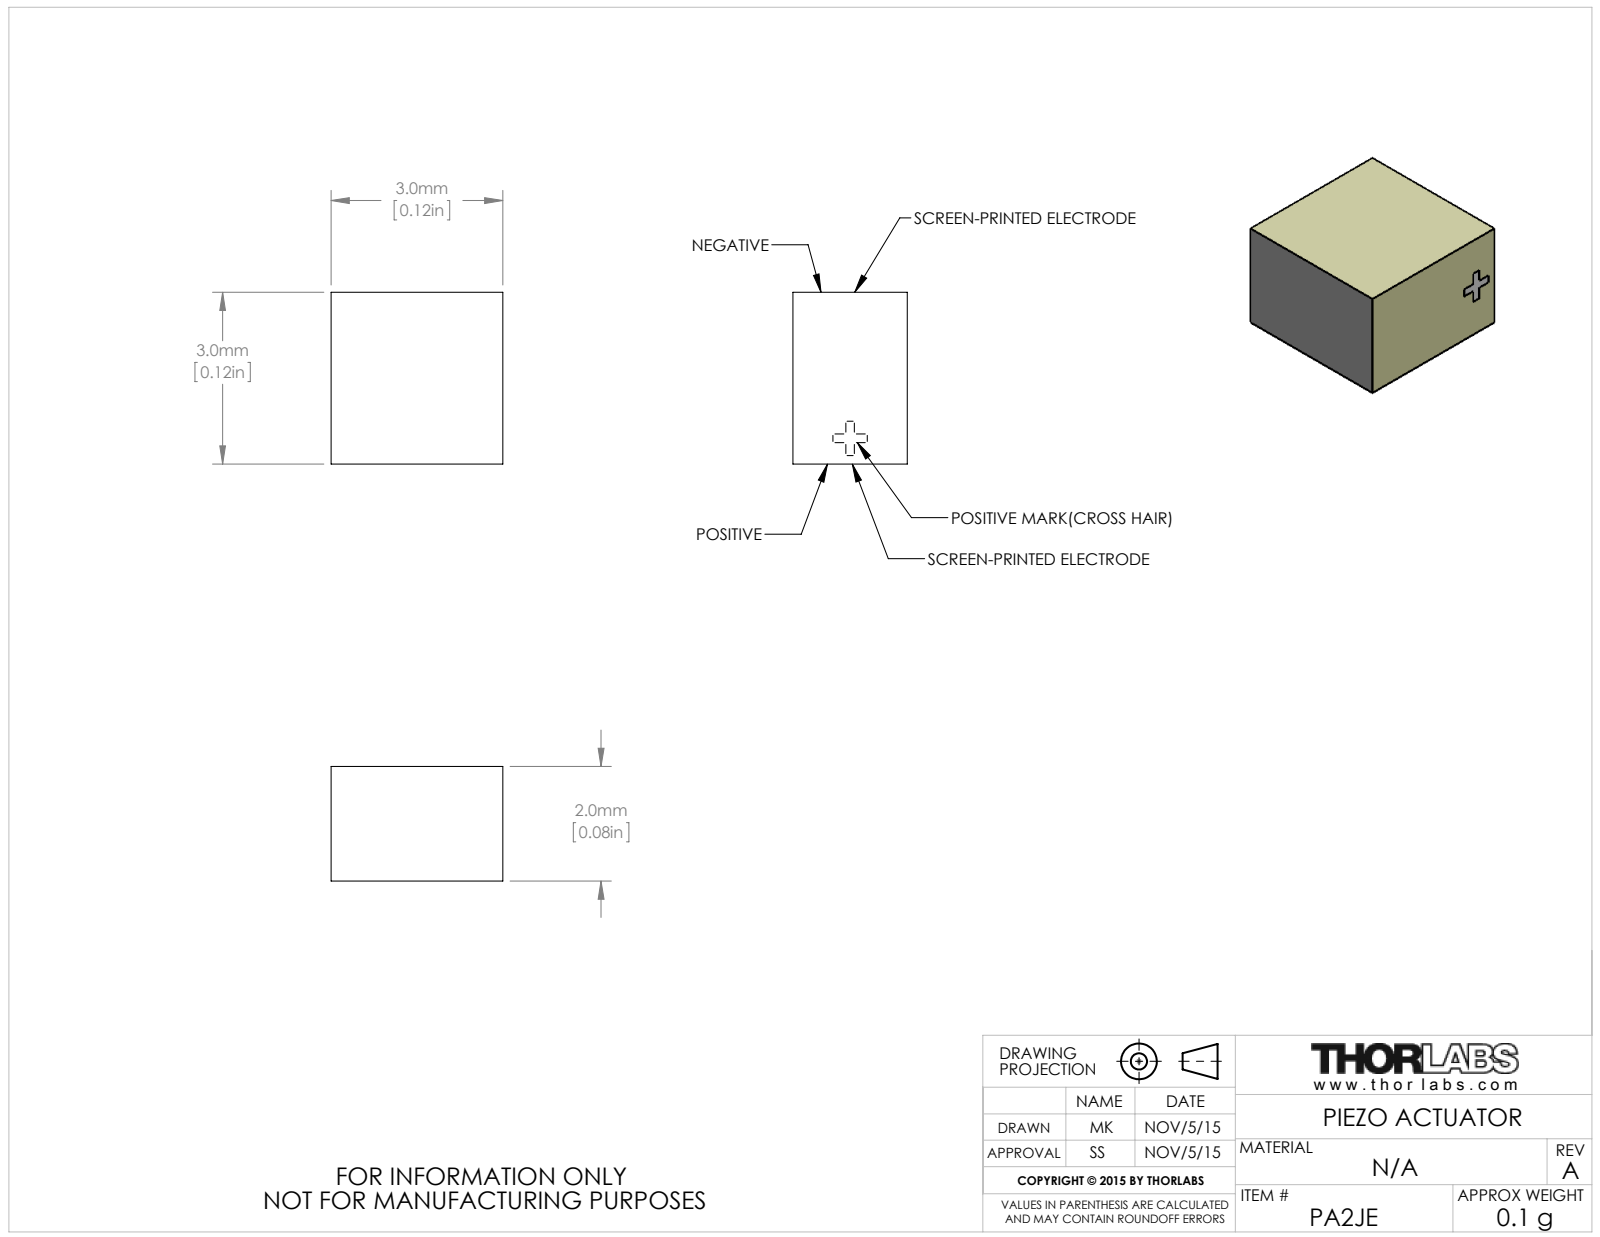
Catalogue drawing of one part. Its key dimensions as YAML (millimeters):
part_name: "CTN003181"
step_written_by: "SolidWorks 2014 (AUTOMOTIVE_DESIGN)"
units: millimeters
bodies: {solids: 1, faces: 7, planar: 7, cylindrical: 0, other: 0}
overall_size: [3, 3, 2]
volume: 18
surface_area: 42
face_to_face_distances: [3, 2]
